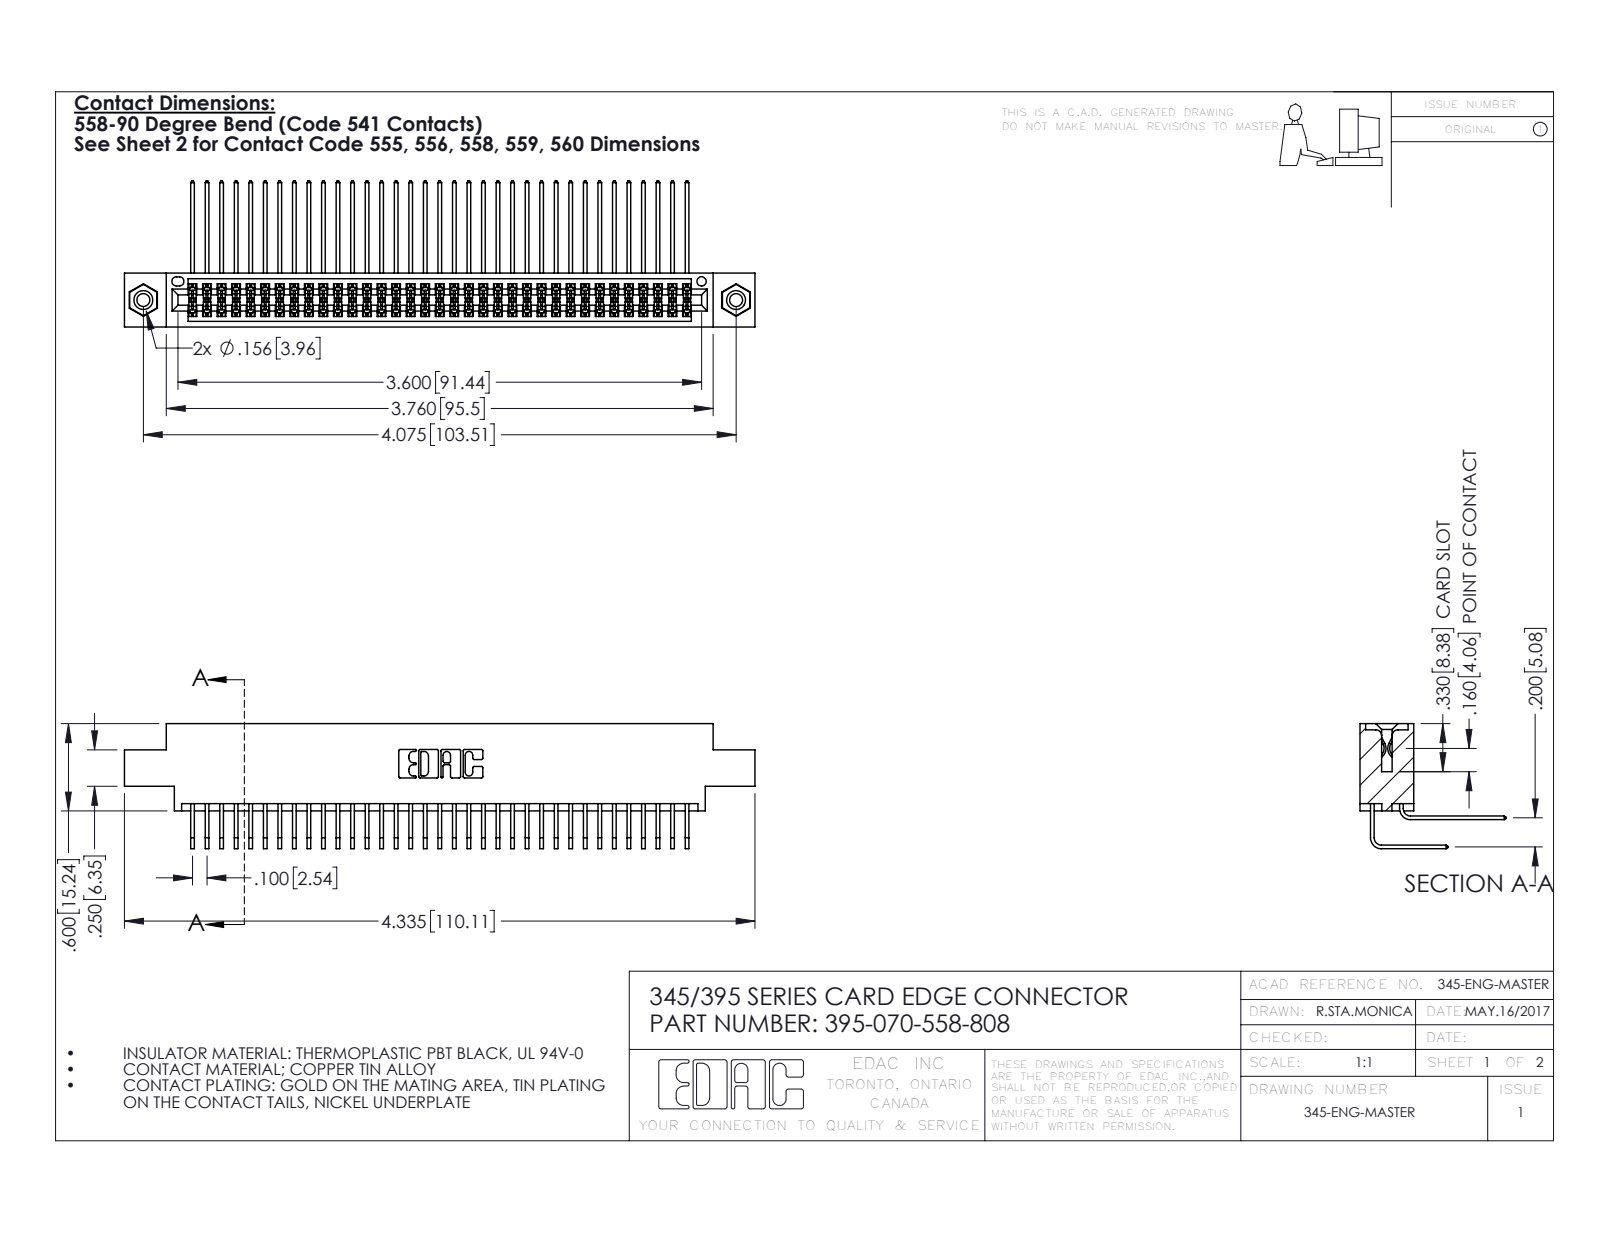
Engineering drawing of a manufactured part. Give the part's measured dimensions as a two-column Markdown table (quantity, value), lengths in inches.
| quantity | value |
| --- | --- |
| part name | 345-292-001_558 559 Tail - 1; 345 Part_0.170 Offset - 0.156 Dia-TI; 345-292-001_558 Tail - 2; 345-250-001_345-250-003-102 (+1 more) |
| STEP written by | SolidWorks 2016 (CONFIG_CONTROL_DESIGN) |
| units | inches |
| bodies | 73 solids, 3830 faces (2566 planar, 1248 cylindrical, 16 other) |
| overall size | 4.335 × 1.005 × 0.859 |
| volume | 0.666 in³ |
| surface area | 27.98 in² |
| round holes (diameter × count) | 0.089 × 2, 0.125 × 2, 0.156 × 2, 0.064 × 1 |
| round bosses / shafts (diameter × count) | 0.155 × 2 |
| partial cylindrical surfaces (radius × count) | 0.006 × 106, 0.01 × 22, 0.007 × 6, 0.031 × 6, 0.026 × 3, 0.014 × 2, 0.019 × 2, 0.022 × 2 |
| main face-to-face distances | 0.072, 0.298, 0.2, 0.37, 0.098, 0.272, 0.025, 0.225, 0.175, 0.025 |
| hole center spacings | 0.27, 3.839, 4.075 |
